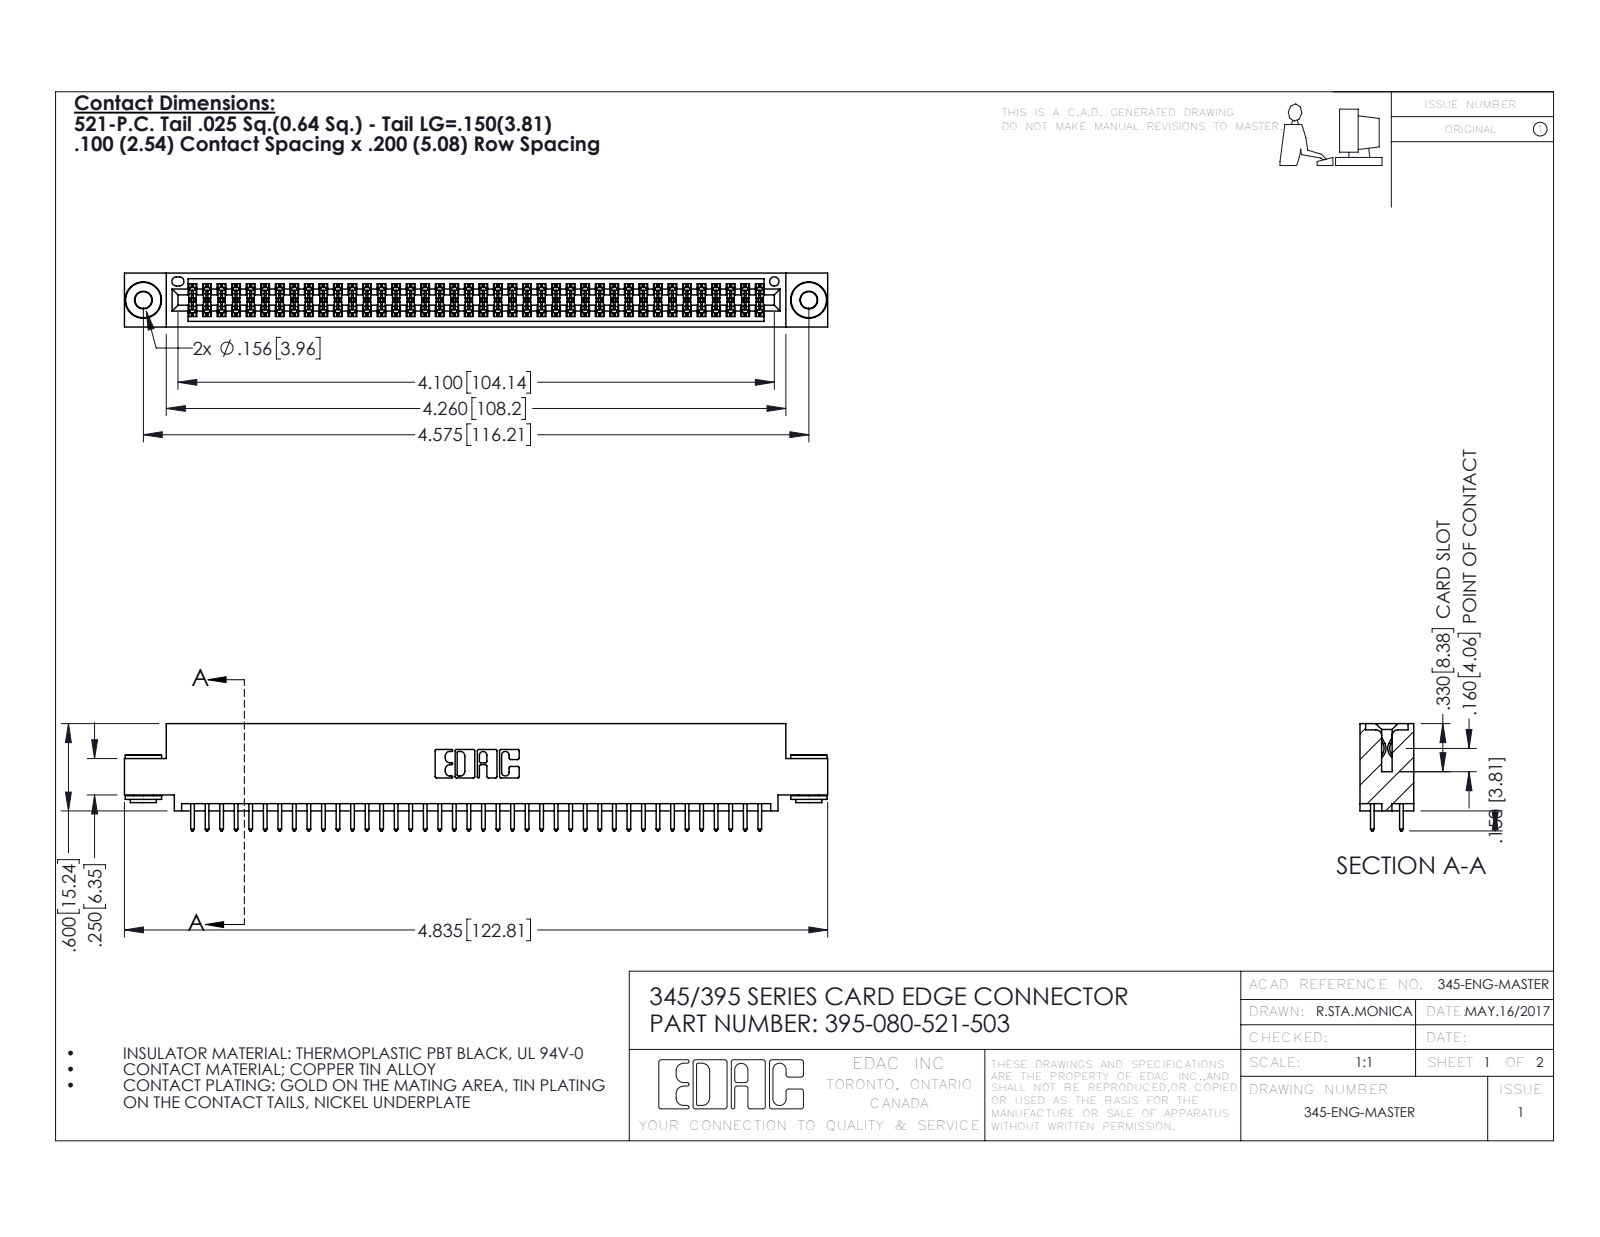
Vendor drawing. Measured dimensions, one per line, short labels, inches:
name: 345-292-001_345-293-121; 395-080-521-503; 345 Part_0.110 Offset - 0.156 Dia-TH; 345-250-002_345-250-002-102
written by: SolidWorks 2016 (CONFIG_CONTROL_DESIGN)
unit: in
bodies: 83 solids, 4168 faces (2734 planar, 1426 cylindrical, 8 other)
size: 4.835 × 0.737 × 0.37
volume: 0.722 in³; area: 27.16 in²
holes: 2× ⌀0.116, 2× ⌀0.156, 1× ⌀0.064
bosses: 2× ⌀0.25, 2× ⌀0.18, 2× ⌀0.136
rounds: 120× R0.006, 80× R0.01, 22× R0.01, 6× R0.007, 6× R0.031, 3× R0.026, 2× R0.014, 2× R0.019
face distances: 0.072, 0.298, 0.2, 0.025, 0.37, 0.098, 0.272, 0.225, 0.175, 0.149
hole spacings: 0.27, 4.339, 4.575
